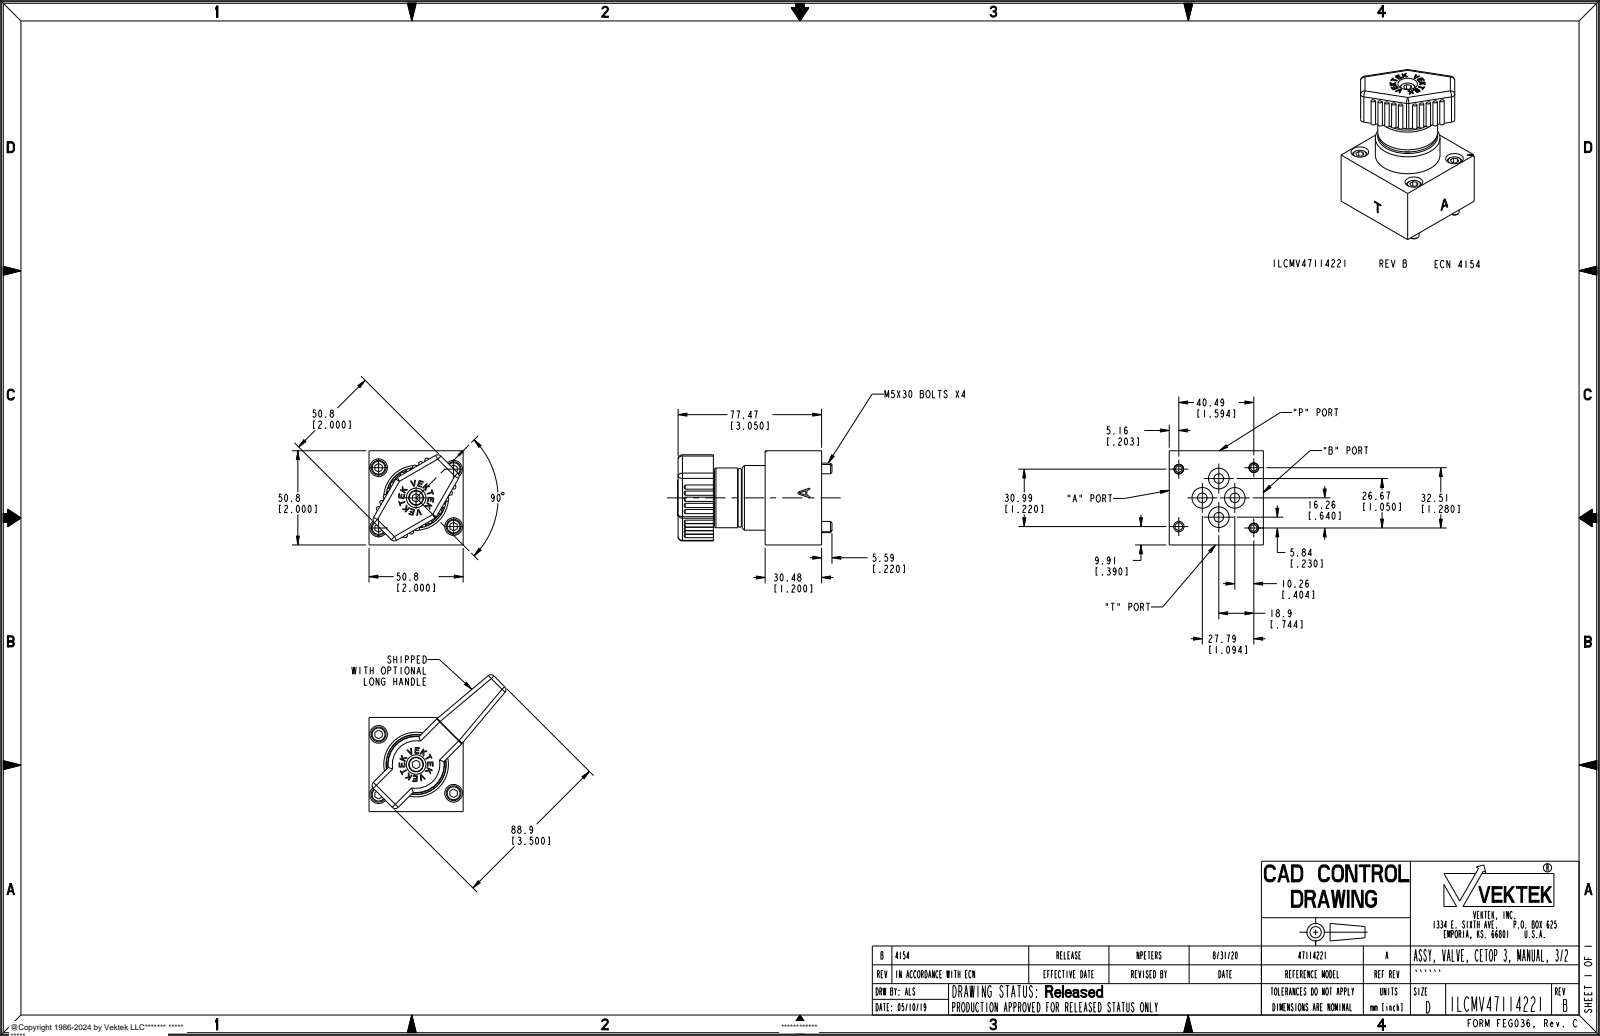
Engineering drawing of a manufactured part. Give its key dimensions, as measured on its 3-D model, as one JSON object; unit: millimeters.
{"part_name": "ILCMV47114221_BASE; ILCMV47114221_ADAPTER; 85600903; 85600902 (+1 more)", "step_written_by": "PRO/ENGINEER BY PARAMETRIC TECHNOLOGY CORPORATION, 2013320 (AP203_CONFIGURATION_CONTROLLED_3D_DESIGN_OF_MECHANICAL_PARTS_AND_ASSEMBLIES_MIM_LF)", "units": "millimeters", "bodies": {"solids": 5, "faces": 1642, "planar": 1374, "cylindrical": 186, "other": 82}, "overall_size": [83.3, 73.9, 73.9], "volume_mm3": 137100, "surface_area_mm2": 39140, "round_holes": [[5.2, 8], [9.5, 4], [11.1, 4], [5.1, 3], [5.1, 2], [5.2, 1], [5.2, 1], [10.5, 1], [12.7, 1]], "round_bosses_or_shafts": [[8, 4], [5, 3], [34.9, 1], [32.3, 1], [7.9, 1], [5.6, 1], [4.8, 1]], "partial_cylinders_radius": [[2.3, 23], [1.2, 20], [2.4, 12], [0.8, 10], [1.1, 8], [1.6, 8], [0.8, 6], [3, 4]], "face_to_face_distances": [50.8, 30.5, 8.1, 27.9, 58.4, 2.5, 19.1, 36.1, 66.5, 10.8], "hole_center_spacings": [10.5, 11.1, 13.5, 13.7, 19.2, 19.8, 20, 22.2]}
